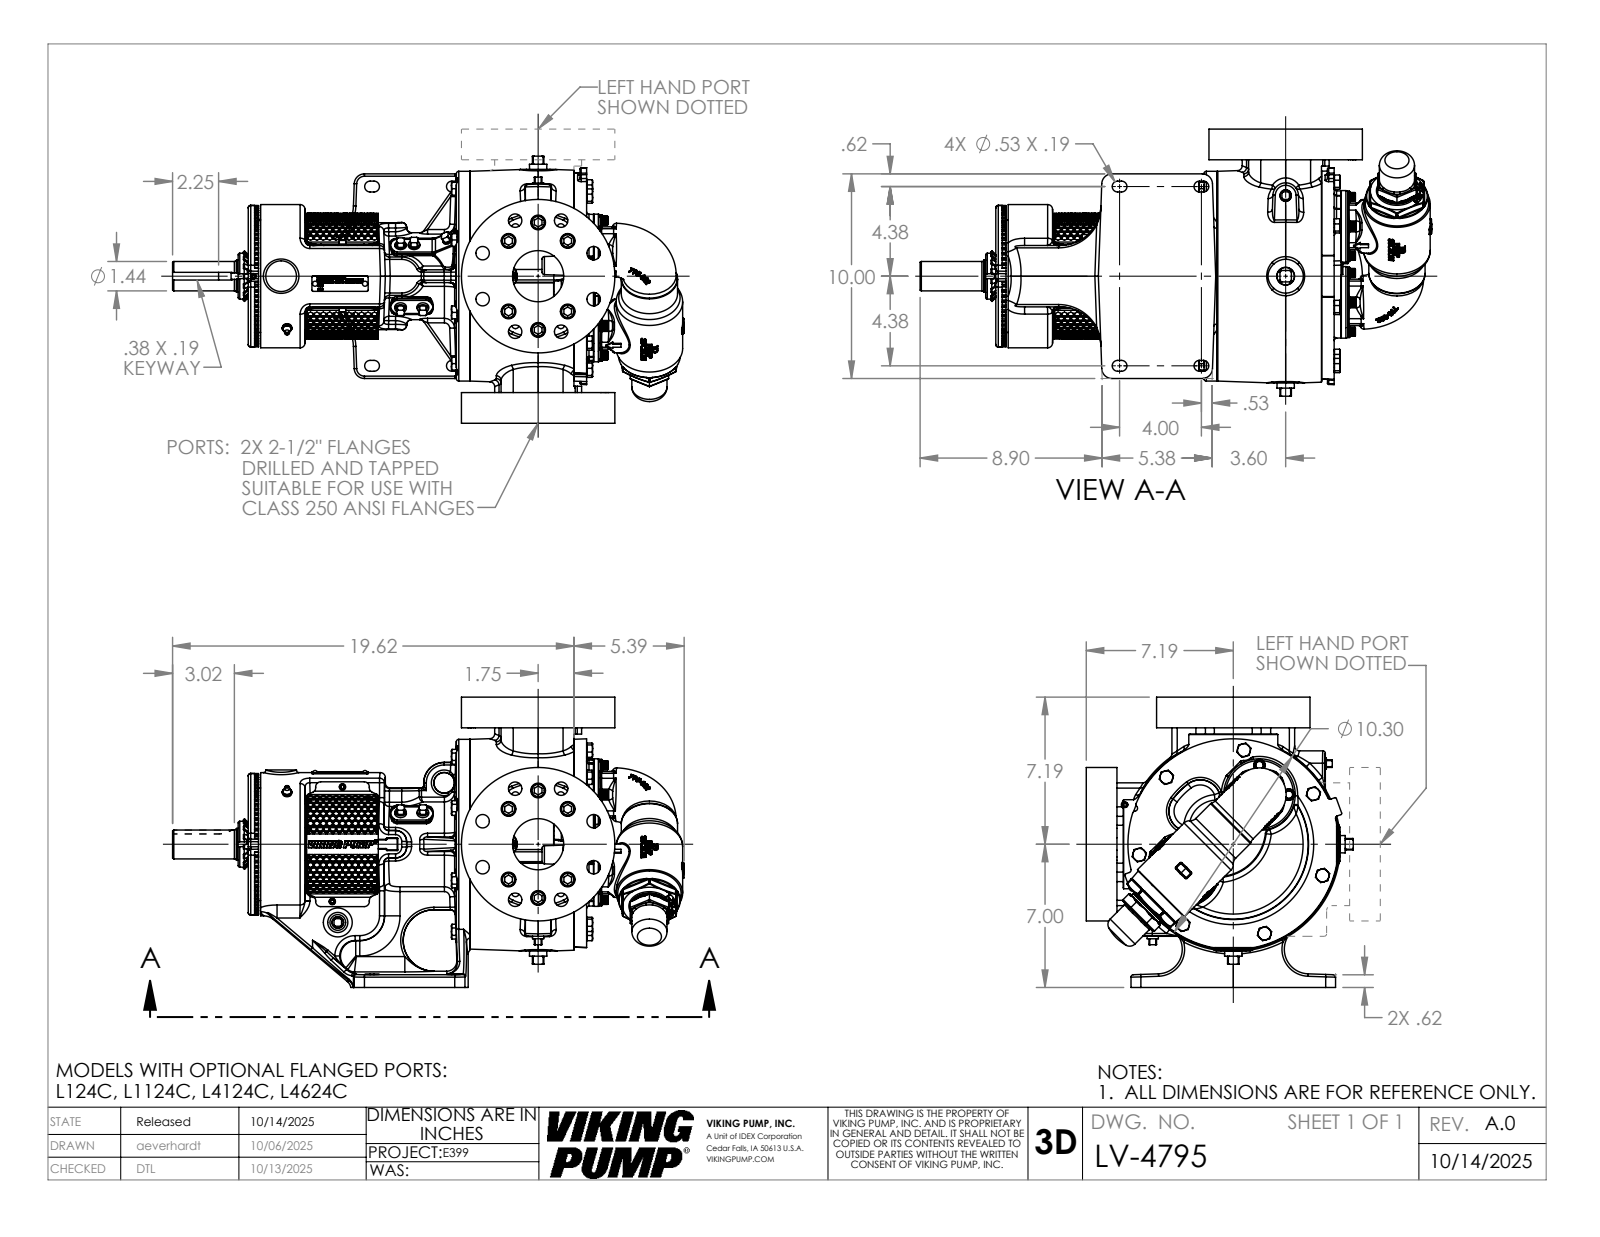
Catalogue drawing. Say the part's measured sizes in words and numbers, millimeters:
The part is named "LV-4795". Its 3-D file was written by "SolidWorks 2024 (AUTOMOTIVE_DESIGN)". It is 1 solid with 5766 faces: 1934 planar, 1227 cylindrical and 2605 other. Overall it measures 635.3 by 360.4 by 331.5 millimeters. Its volume is 16 670 000 cubic millimeters and its surface area 987 700 square millimeters. Round holes: 16 of diameter 16.7, 12 of diameter 18.3, 9 of diameter 6.4, 8 of diameter 10.3, 8 of diameter 10.4, 8 of diameter 27.8, 6 of diameter 5.1, 3 of diameter 4, 2 of diameter 6.8, 2 of diameter 8, 2 of diameter 63.5, 1 of diameter 4. Round bosses or shafts: 12 of diameter 16.8, 9 of diameter 15.9, 8 of diameter 14.3, 6 of diameter 15.9, 4 of diameter 9.5, 4 of diameter 9.5, 3 of diameter 88.9, 3 of diameter 7.9. Partial cylindrical surfaces (rounded edges, fillets, slot ends): 109 of radius 1.6, 76 of radius 3, 74 of radius 1.8, 48 of radius 6.1, 36 of radius 0.8, 16 of radius 11.4, 16 of radius 25.4, 12 of radius 1.5. The main face-to-face distances are 38.1, 360.3, 322.2, 350.3, 89.8, 260.5, 12.7, 57.2, 54.4, 144.3. The hole center spacings are 76.2, 57.1, 74.6, 137.9, 26.4, 35.6, 51.6, 51.6.
